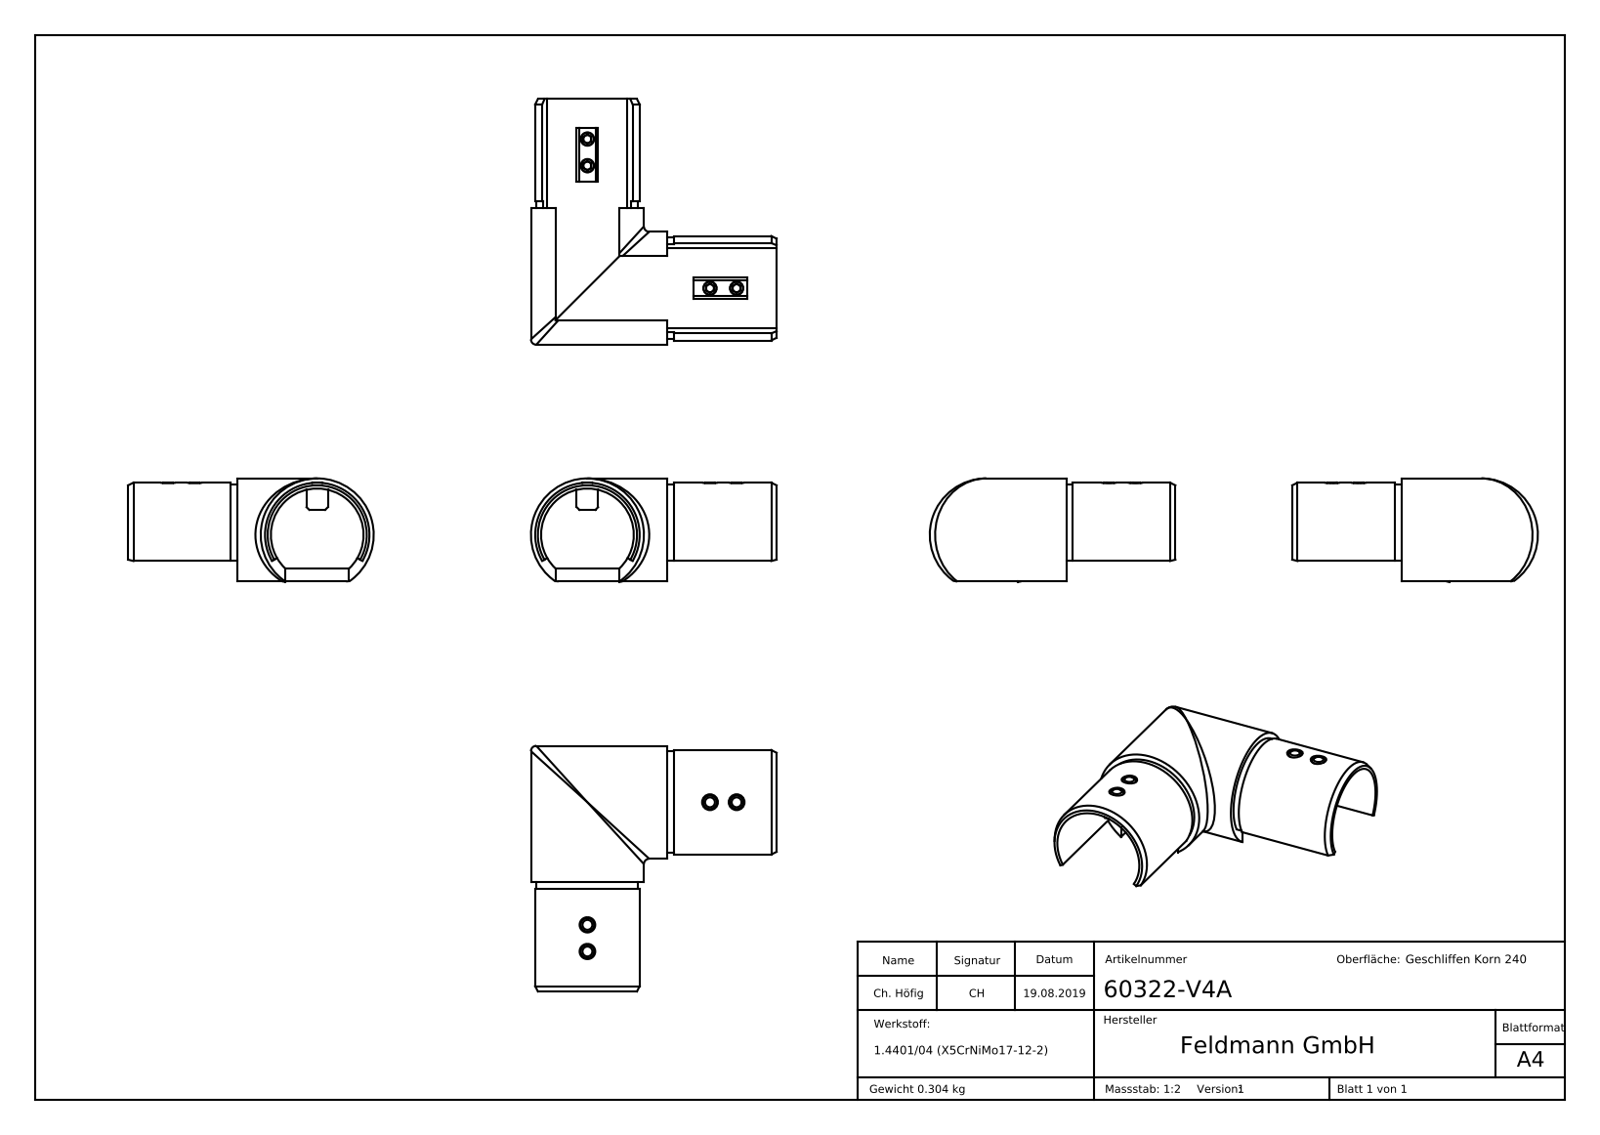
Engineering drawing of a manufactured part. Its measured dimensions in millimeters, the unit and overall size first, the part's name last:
Units: millimetres
Overall size (bounding box): 92.2 × 92.2 × 38.87
Round holes (diameter × count): ⌀5 ×4
Round bosses / shafts (diameter × count): ⌀6 ×4, ⌀42.4 ×2
Partial cylindrical surfaces — rounded edges, fillets, slot ends (radius × count): R17.4 ×2, R19.1 ×2, R19.6 ×2
Main face-to-face distances: 8, 16, 42, 34, 26, 59, 83, 75, 67, 41
Hole centre spacings: 10, 72.47, 65.05, 79.2
Volume: 37 974 mm³ · Surface area: 28 094 mm²
Bodies: 5 solids, 387 faces (215 planar, 40 cylindrical, 132 other)
Part name (STEP PRODUCT): 60322-V4A; DIN913_DIN 913 M6x10; 6032X-240 Teil1 Konfig Verlaufecke Nutrohr_60322-V4A Teil1
STEP written by: SolidWorks 2015 (CONFIG_CONTROL_DESIGN)
